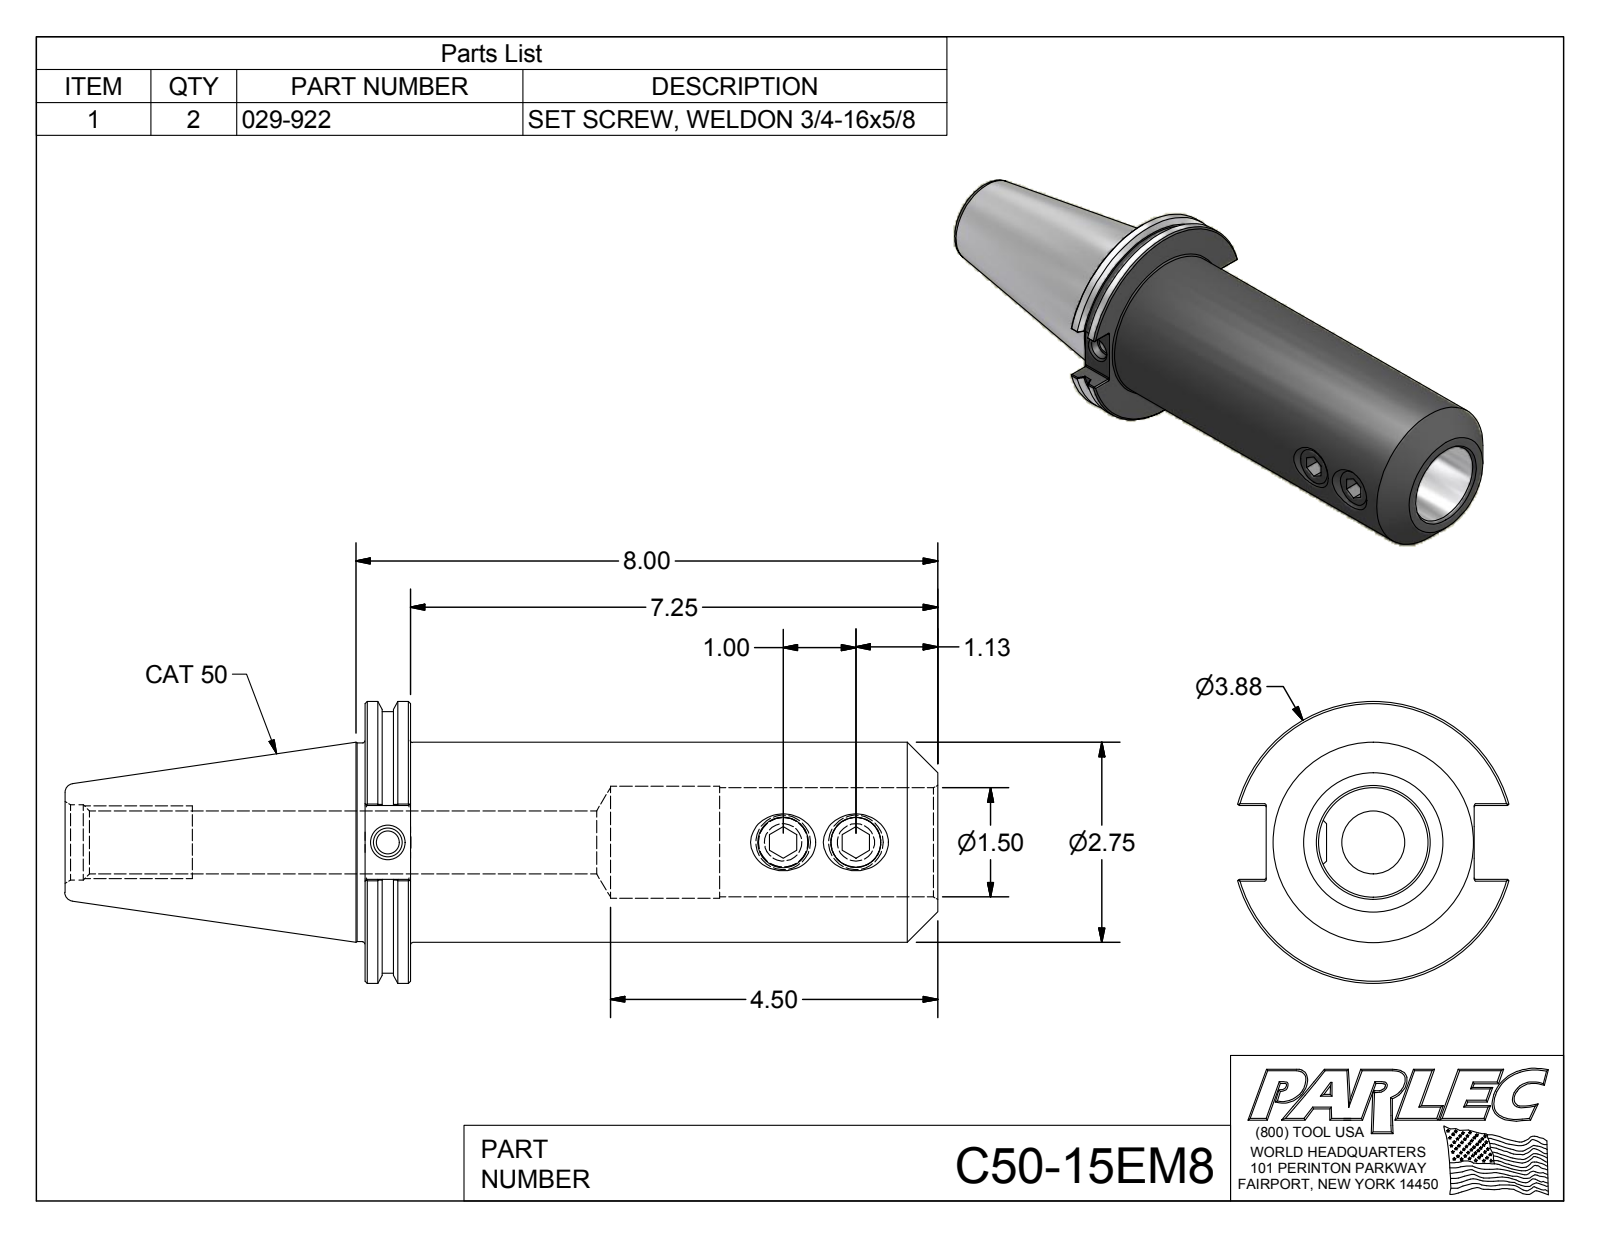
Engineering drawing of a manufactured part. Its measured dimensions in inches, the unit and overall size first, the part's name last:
Units: inches
Overall size (bounding box): 12 × 3.875 × 3.729
Round holes (diameter × count): ⌀0.682 ×2, ⌀0.315 ×1, ⌀0.399 ×1, ⌀0.865 ×1, ⌀1.038 ×1, ⌀1.5 ×1, ⌀1.54 ×1
Round bosses / shafts (diameter × count): ⌀0.75 ×2, ⌀3.875 ×1, ⌀3.594 ×1, ⌀2.75 ×1, ⌀2.73 ×1
Partial cylindrical surfaces — rounded edges, fillets, slot ends (radius × count): R0.02 ×12
Main face-to-face distances: 0.625, 7.875, 7.25, 0.03, 4.125, 4.75, 12, 2.86, 0.375, 1.015
Hole centre spacings: 1, 5.435, 6.435
Volume: 51.88 in³ · Surface area: 163.1 in²
Bodies: 3 solids, 115 faces (51 planar, 30 cylindrical, 34 other)
Part name (STEP PRODUCT): C50-15EM8; C50-15EM8-1; 029-922
STEP written by: Autodesk Inventor 2012 (AUTOMOTIVE_DESIGN)
